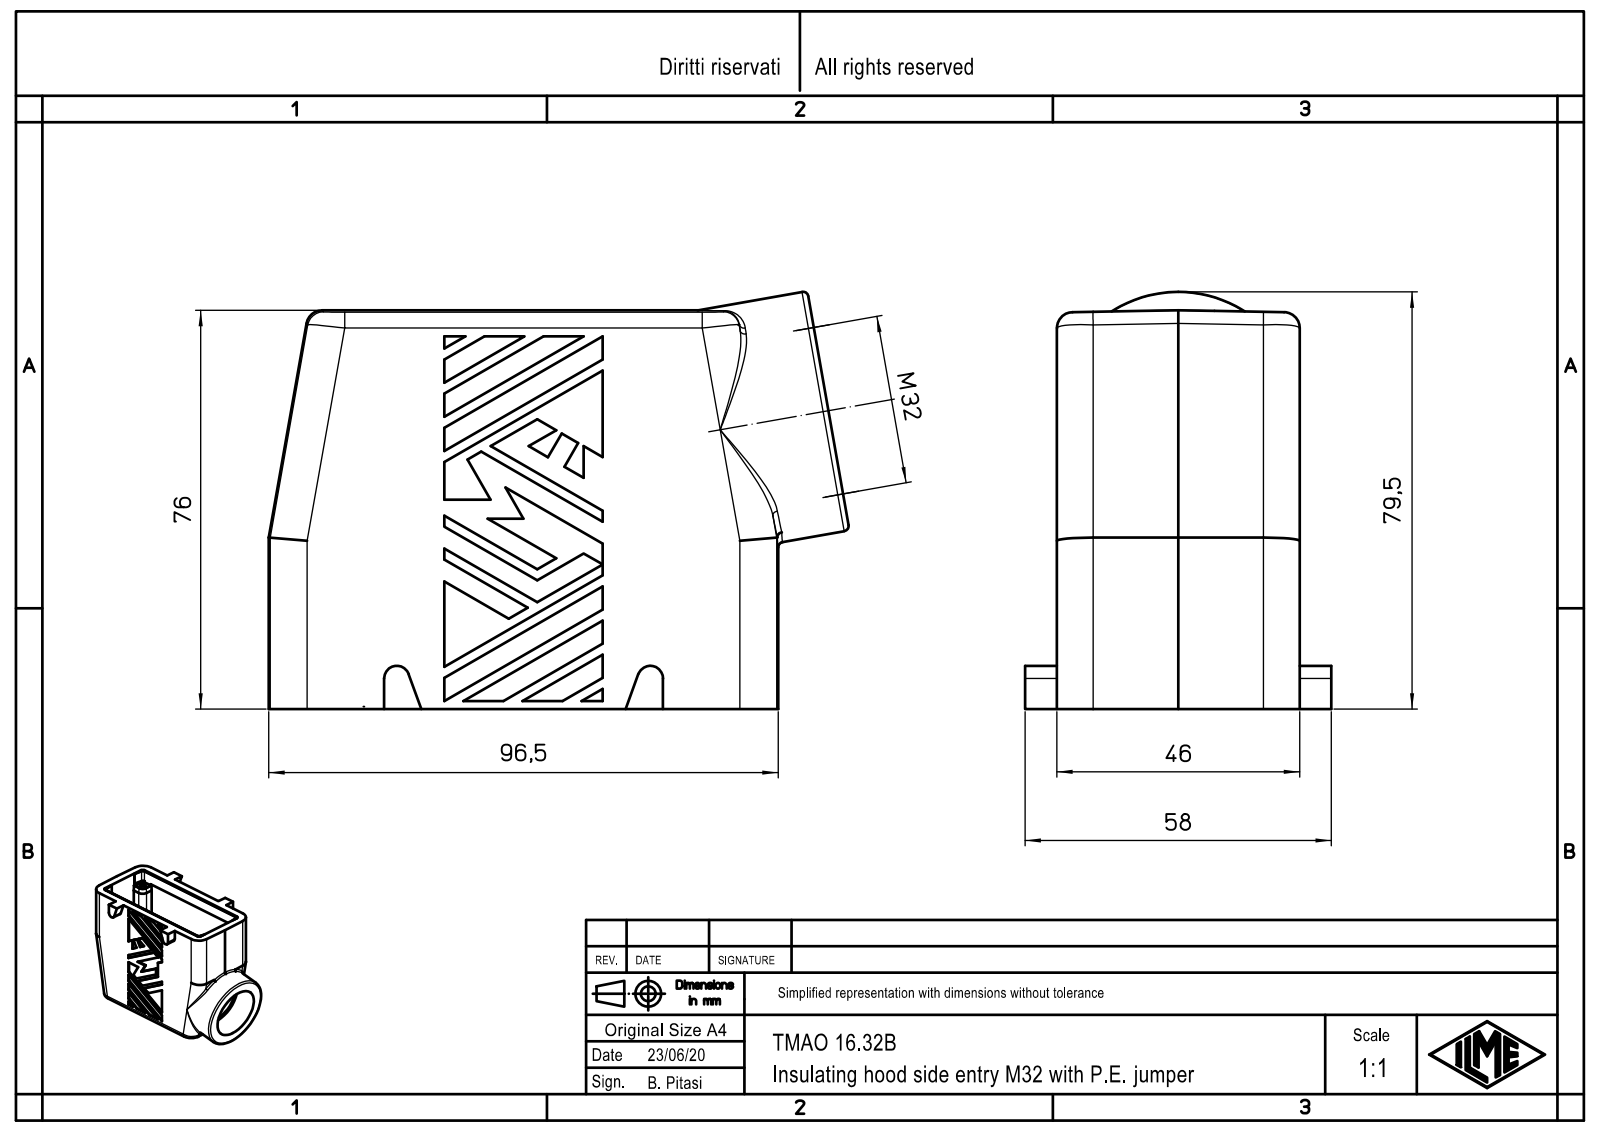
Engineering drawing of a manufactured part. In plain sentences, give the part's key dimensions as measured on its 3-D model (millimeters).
The part is named "TMAO_16.32B". Its 3-D file was written by "Creo Elements/Direct Modeling 20.1B 02-Apr-2019 (C) Parametric Technology GmbH (AUTOMOTIVE_DESIGN)". It is 1 solid with 471 faces: 300 planar, 83 cylindrical and 88 other. Overall it measures 109.83 by 78.98 by 58 millimeters. Its volume is 138 456 cubic millimeters and its surface area 51 542 square millimeters. Round holes: 4 of diameter 3, 4 of diameter 3.5, 1 of diameter 28, 1 of diameter 32. Round bosses or shafts: 4 of diameter 4.8, 1 of diameter 46. Partial cylindrical surfaces (rounded edges, fillets, slot ends): 12 of radius 1.5, 8 of radius 7, 6 of radius 3, 4 of radius 1.3, 4 of radius 1.6, 4 of radius 2, 4 of radius 3.5, 2 of radius 2.4. The main face-to-face distances are 46, 0.5, 45.5, 69.99, 5.6, 45, 39.4, 5.3, 5.8, 40.2. The hole center spacings are 27, 77.5, 82.07.
